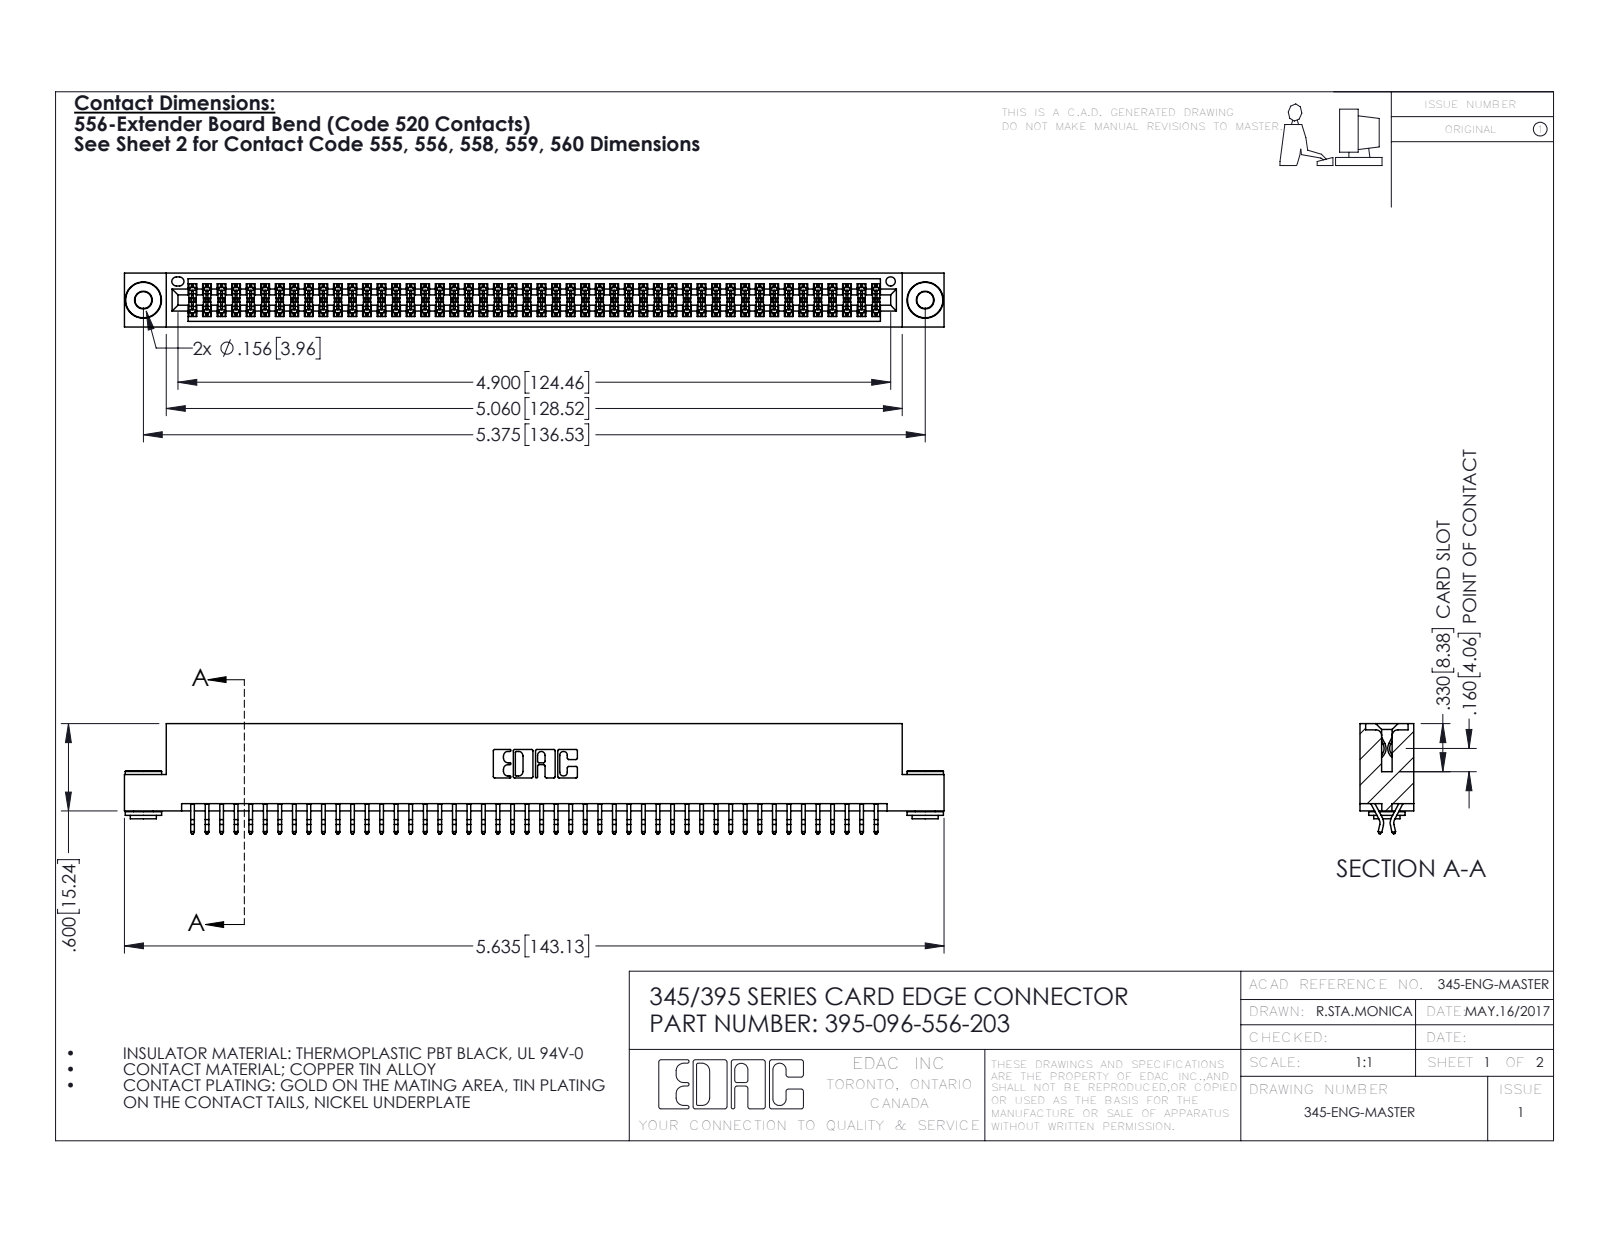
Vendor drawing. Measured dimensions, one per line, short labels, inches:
name: 345 Part_Flush Mounting Lugs - 0.156 Dia-TH; 345-250-002_345-250-002-102; 345-292-001_556 Tail; 395-096-556-203
written by: SolidWorks 2016 (CONFIG_CONTROL_DESIGN)
unit: in
bodies: 99 solids, 5540 faces (3642 planar, 1890 cylindrical, 8 other)
size: 5.635 × 0.757 × 0.37
volume: 0.853 in³; area: 32.39 in²
holes: 2× ⌀0.116, 2× ⌀0.156, 1× ⌀0.064
bosses: 2× ⌀0.25, 2× ⌀0.18, 2× ⌀0.136
rounds: 144× R0.006, 22× R0.01, 6× R0.007, 6× R0.031, 3× R0.026, 2× R0.01, 2× R0.014, 2× R0.019
face distances: 0.072, 0.298, 0.37, 0.2, 0.025, 0.098, 0.272, 0.225, 0.175, 0.149
hole spacings: 0.27, 5.139, 5.375
